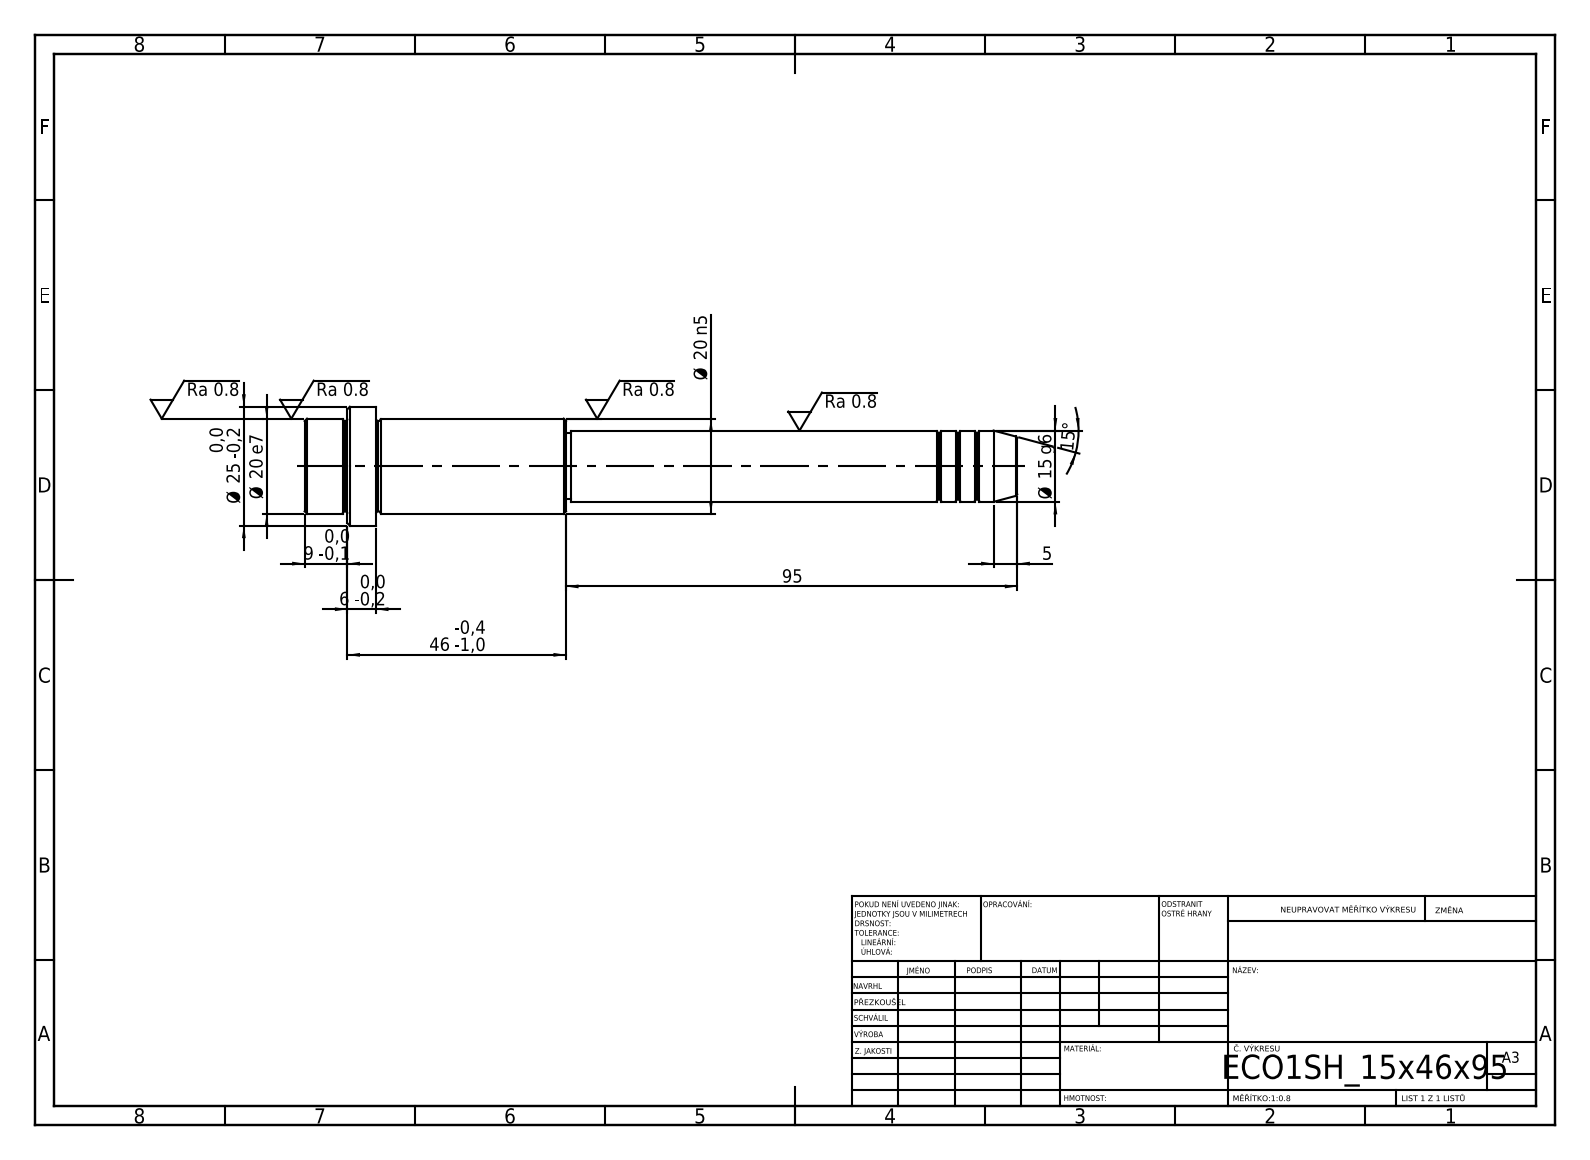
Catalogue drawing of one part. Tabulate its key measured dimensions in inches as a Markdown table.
| quantity | value |
| --- | --- |
| STEP written by | SolidWorks 2019 (CONFIG_CONTROL_DESIGN) |
| units | inches |
| bodies | 1 solid, 52 faces (6 planar, 16 cylindrical, 30 other) |
| overall size | 5.906 × 0.984 × 0.984 |
| volume | 2.125 in³ |
| surface area | 14.03 in² |
| round bosses / shafts (diameter × count) | 0.984 × 1, 0.787 × 1, 0.591 × 1, 0.551 × 1 |
| main face-to-face distances | 0.591, 0.236, 0.354, 1.575, 1.811, 2.165, 3.74, 5.315, 5.551, 5.906 |
